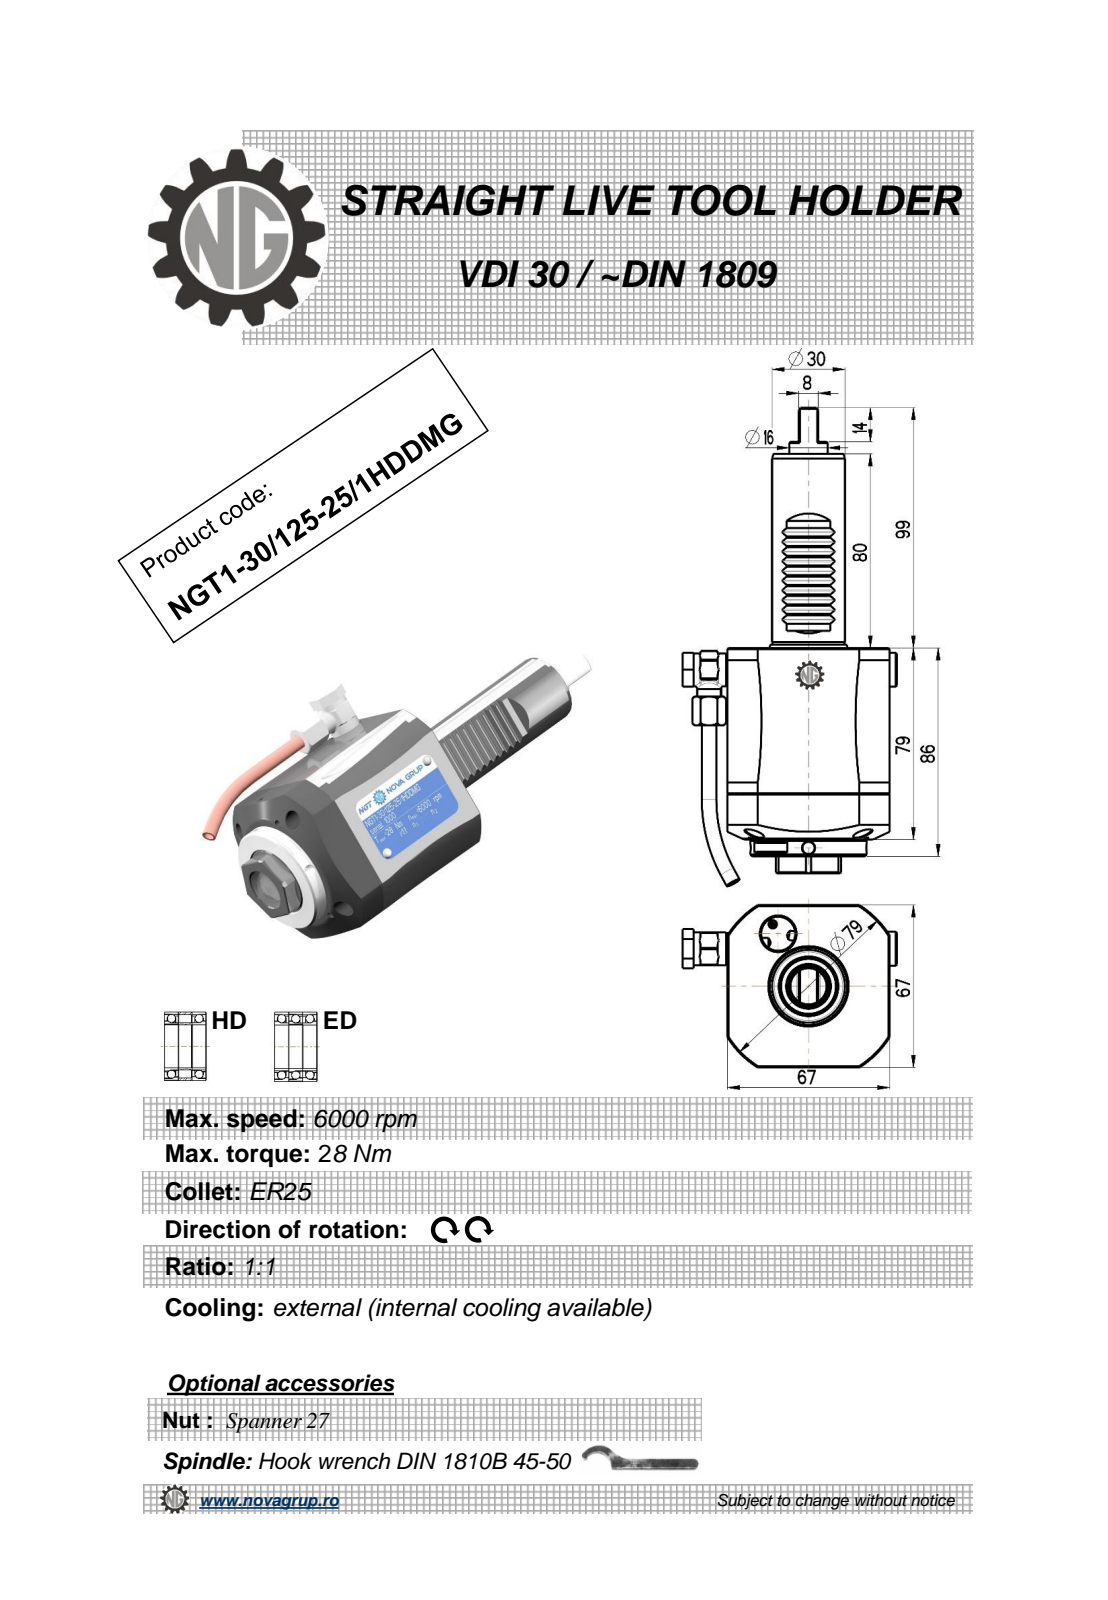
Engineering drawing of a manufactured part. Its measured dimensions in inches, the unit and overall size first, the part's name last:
Units: inches
Overall size (bounding box): 7.769 × 3.48 × 2.638
Round holes (diameter × count): ⌀0.157 ×3, ⌀0.197 ×2, ⌀0.118 ×1, ⌀0.236 ×1, ⌀0.244 ×1, ⌀0.354 ×1, ⌀0.394 ×1, ⌀0.433 ×1, ⌀0.709 ×1, ⌀0.945 ×1, ⌀0.976 ×1, ⌀1.043 ×1
Round bosses / shafts (diameter × count): ⌀1.89 ×1, ⌀1.181 ×1, ⌀0.821 ×1, ⌀0.626 ×1, ⌀0.551 ×1, ⌀0.535 ×1, ⌀0.512 ×1, ⌀0.394 ×1
Partial cylindrical surfaces — rounded edges, fillets, slot ends (radius × count): R0.012 ×10, R0.02 ×4, R0.031 ×2, R0.303 ×1, R1.555 ×1
Main face-to-face distances: 2.638, 0.276, 3.386, 3.11, 0.111, 0.551, 0.223, 0.557, 0.445, 0.846
Hole centre spacings: 0.016, 1.726, 1.741, 2.957
Volume: 24.23 in³ · Surface area: 72.84 in²
Bodies: 2 solids, 367 faces (143 planar, 103 cylindrical, 121 other)
Part name (STEP PRODUCT): NGT1_30_125_25_3EDDMG
STEP written by: PRO/ENGINEER BY PARAMETRIC TECHNOLOGY CORPORATION, 2010280 (CONFIG_CONTROL_DESIGN)
